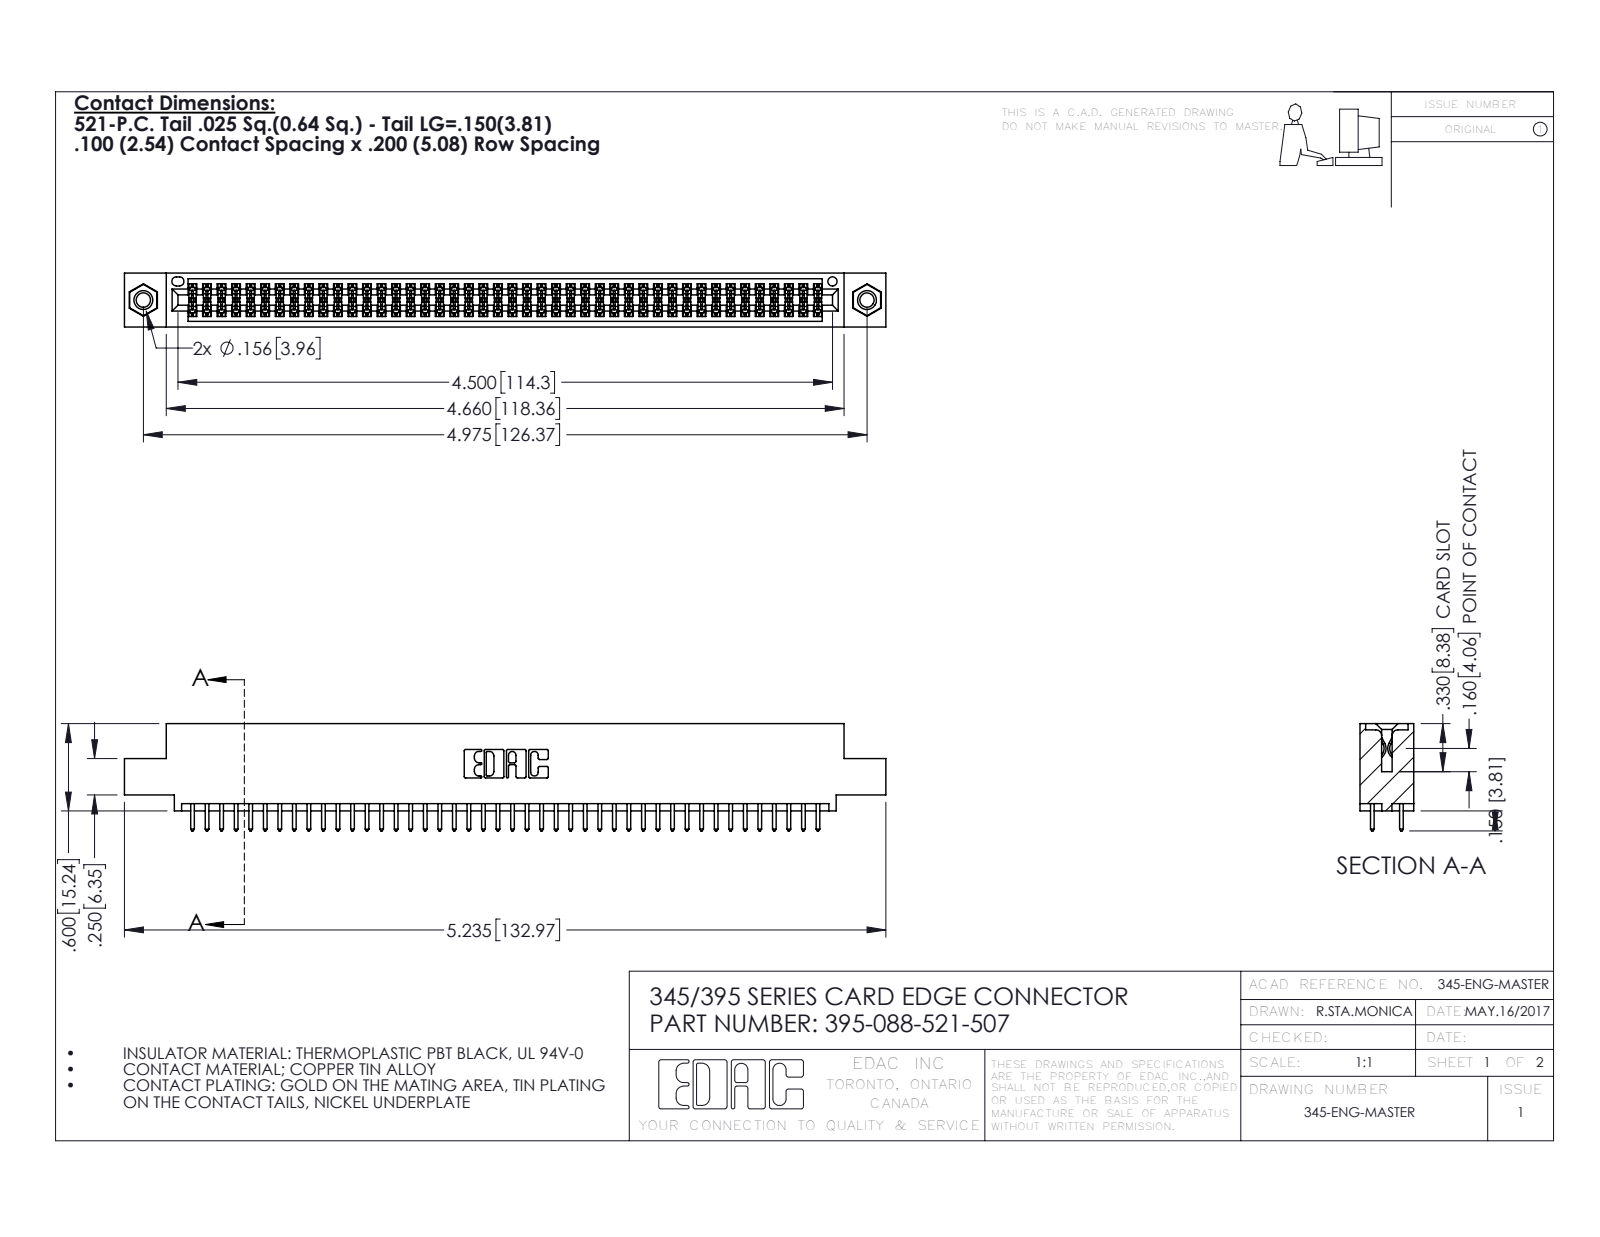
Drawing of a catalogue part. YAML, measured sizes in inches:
part_name: "345-250-001_345-250-005-103; 345 Part_0.110 Offset - 0.156 Dia-TI; 395-088-521-507; 345-292-001_345-293-121"
step_written_by: "SolidWorks 2016 (CONFIG_CONTROL_DESIGN)"
units: inches
bodies: {solids: 91, faces: 4590, planar: 3020, cylindrical: 1554, other: 16}
overall_size: [5.235, 0.737, 0.37]
volume: 0.782
surface_area: 29.24
round_holes:
  - {diameter: 0.098, count: 2}
  - {diameter: 0.125, count: 2}
  - {diameter: 0.156, count: 2}
  - {diameter: 0.064, count: 1}
round_bosses_or_shafts:
  - {diameter: 0.155, count: 2}
partial_cylinders:
  - {radius: 0.006, count: 132}
  - {radius: 0.01, count: 88}
  - {radius: 0.01, count: 22}
  - {radius: 0.007, count: 6}
  - {radius: 0.031, count: 6}
  - {radius: 0.026, count: 3}
  - {radius: 0.014, count: 2}
  - {radius: 0.019, count: 2}
face_to_face_distances: [0.072, 0.298, 0.2, 0.37, 0.098, 0.272, 0.025, 0.225, 0.175, 0.149]
hole_center_spacings: [0.27, 4.739, 4.975]
